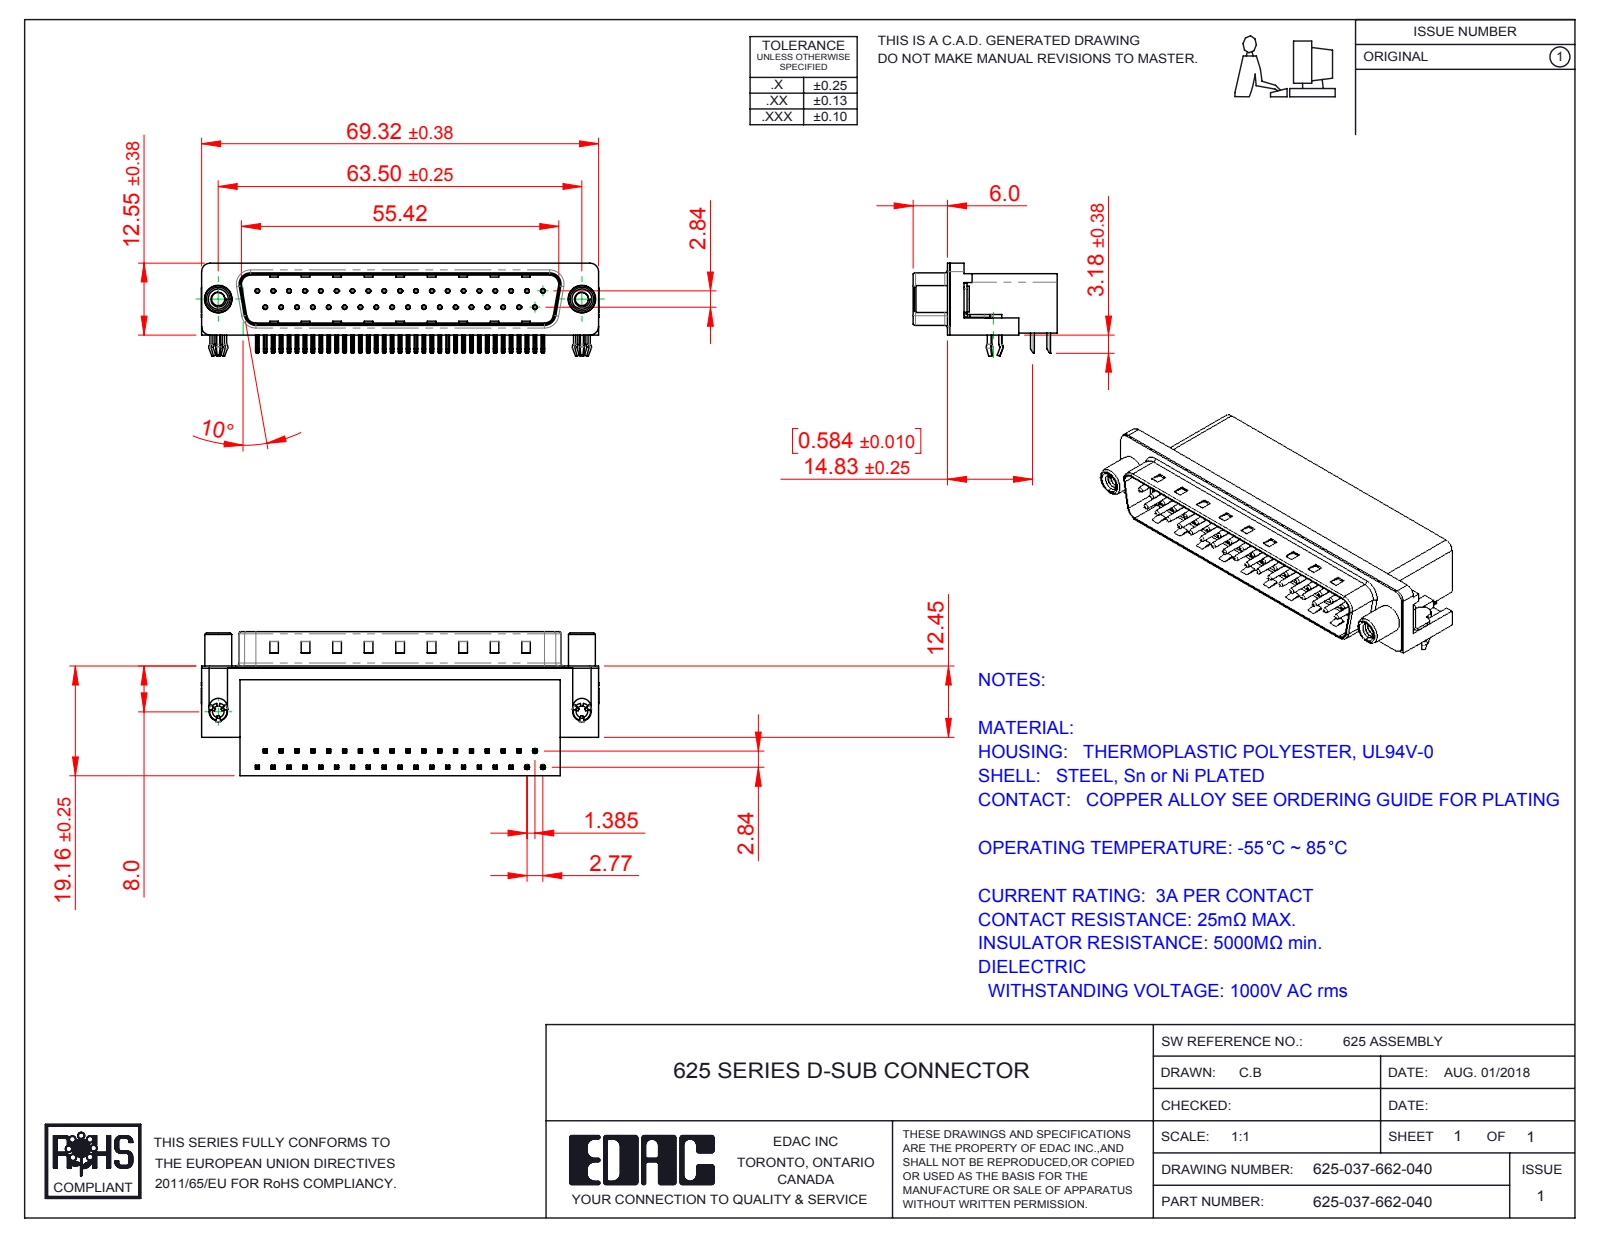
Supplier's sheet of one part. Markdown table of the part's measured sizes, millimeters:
| quantity | value |
| --- | --- |
| part name | 625 Contact Top; 625 Shell_37 Socket; 625 Housing_37 Socket; 625 3 Prong Board Lock (+3 more) |
| STEP written by | SolidWorks 2016 (CONFIG_CONTROL_DESIGN) |
| units | millimeters |
| bodies | 43 solids, 3299 faces (2043 planar, 931 cylindrical, 325 other) |
| overall size | 69.4 × 25.16 × 16.25 |
| volume | 12 700 mm³ |
| surface area | 12 014 mm² |
| round holes (diameter × count) | 0.35 × 37, 0.8 × 37, 2 × 2, 2.3 × 2, 3.1 × 2, 4 × 2, 4.8 × 2, 5 × 2 |
| round bosses / shafts (diameter × count) | 0.75 × 37, 4.9 × 2, 4.7 × 2, 4.5 × 2, 3.85 × 2, 3 × 2 |
| partial cylindrical surfaces (radius × count) | 0.25 × 152, 0.12 × 74, 1 × 16, 0.5 × 9, 1.6 × 8, 1.5 × 7, 0.9 × 4, 2 × 4 |
| main face-to-face distances | 10.34, 0.4, 18.76, 8.76, 2.84, 19.16, 2.09, 10.1, 1.74, 8.36 |
| hole center spacings | 3.16, 2.77, 5.54, 8.31, 11.08, 13.85, 19.39, 22.16 |
